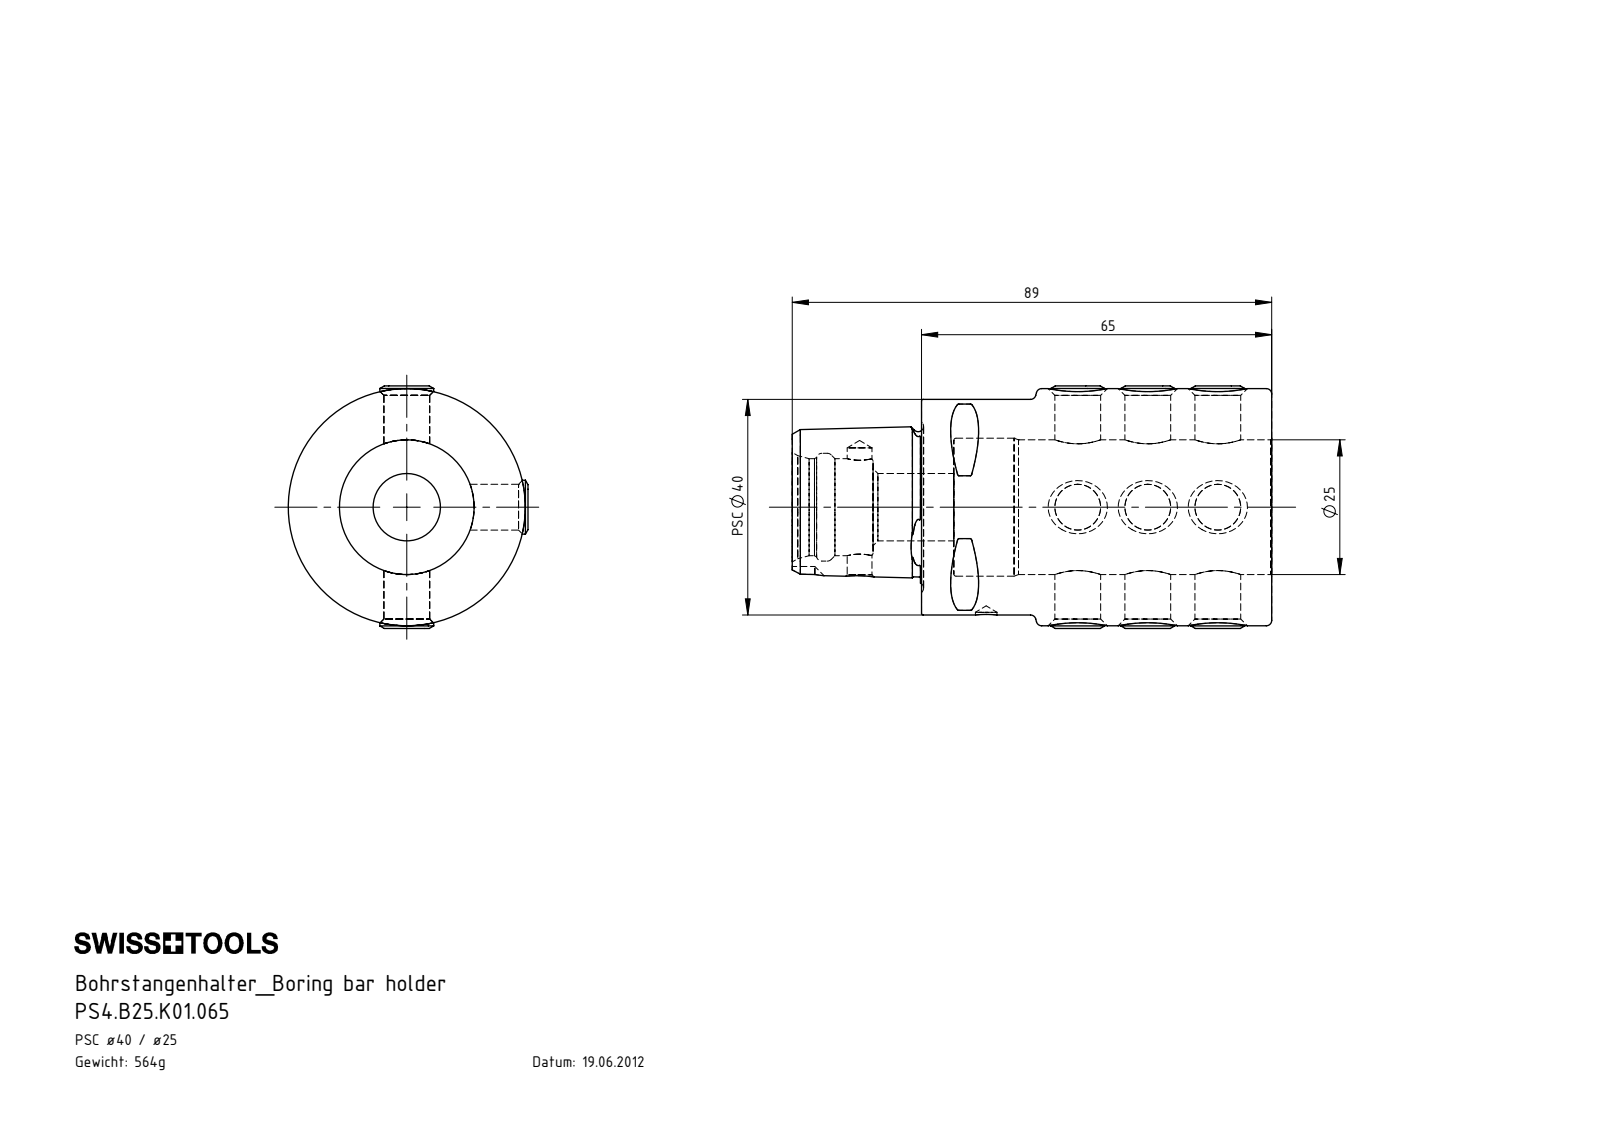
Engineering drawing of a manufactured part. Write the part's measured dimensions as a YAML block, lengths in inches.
part_name: "ISO 4026 - M10 x 10_PreviewCfg; PS4.B25.K01.065; PS4-B25.K01.065_A"
step_written_by: "SolidWorks 2017 (AUTOMOTIVE_DESIGN)"
units: inches
bodies: {solids: 10, faces: 225, planar: 101, cylindrical: 38, other: 86}
overall_size: [3.504, 1.772, 1.752]
volume: 4.387
surface_area: 39.61
round_holes:
  - {diameter: 0.335, count: 6}
  - {diameter: 0.157, count: 1}
  - {diameter: 0.181, count: 1}
  - {diameter: 0.492, count: 1}
  - {diameter: 0.709, count: 1}
  - {diameter: 0.787, count: 1}
  - {diameter: 0.984, count: 1}
  - {diameter: 1.008, count: 1}
round_bosses_or_shafts:
  - {diameter: 0.394, count: 6}
  - {diameter: 1.732, count: 1}
  - {diameter: 1.575, count: 1}
partial_cylinders:
  - {radius: 0.012, count: 8}
  - {radius: 0.118, count: 1}
face_to_face_distances: [0.236, 0.197, 2.559, 2.323, 0.394, 1.378, 0.157, 0.945, 1.181, 3.504]
hole_center_spacings: [0.512, 1.024, 0.669, 0.925, 1.181, 1.594, 1.693, 2.106]
